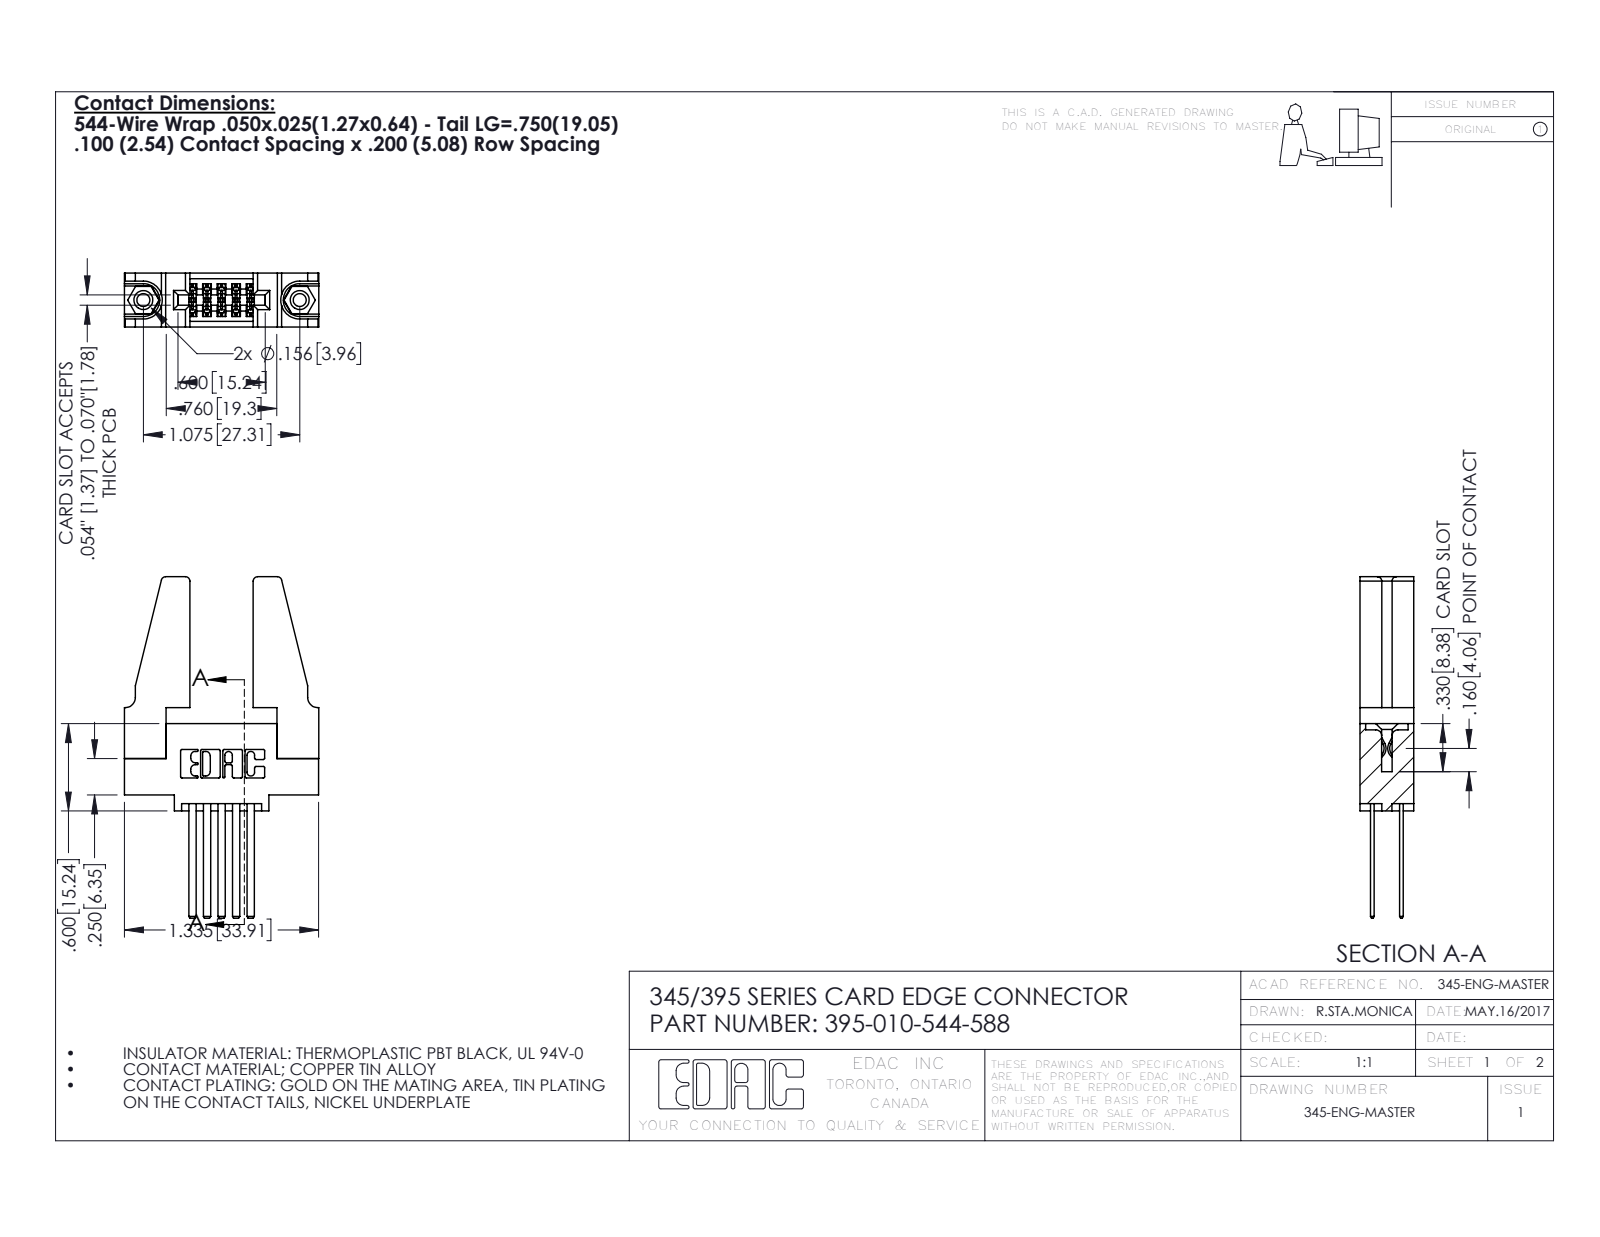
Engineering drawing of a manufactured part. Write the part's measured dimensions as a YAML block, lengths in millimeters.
part_name: "345-220-078_345-220-088; 345 Part_0.110 Offset - 0.156 Dia-TH; 345-250-001_345-250-001-102; 345-292-001_345-293-144 (+1 more)"
step_written_by: "SolidWorks 2016 (CONFIG_CONTROL_DESIGN)"
units: millimeters
bodies: {solids: 15, faces: 694, planar: 446, cylindrical: 232, other: 16}
overall_size: [59.6, 33.9, 9.4]
volume: 6280
surface_area: 7374
round_holes:
  - {diameter: 2.3, count: 2}
  - {diameter: 3.2, count: 2}
  - {diameter: 4, count: 2}
  - {diameter: 1.6, count: 1}
round_bosses_or_shafts:
  - {diameter: 3.9, count: 2}
partial_cylinders:
  - {radius: 0.3, count: 22}
  - {radius: 0.2, count: 15}
  - {radius: 0.8, count: 8}
  - {radius: 0.2, count: 6}
  - {radius: 0.8, count: 6}
  - {radius: 0.7, count: 3}
  - {radius: 0.4, count: 2}
  - {radius: 0.5, count: 2}
face_to_face_distances: [9.4, 1.8, 7.6, 5.1, 2.5, 6.9, 0.6, 5.7, 1.3, 6.4]
hole_center_spacings: [6.9, 21.5, 27.3]
